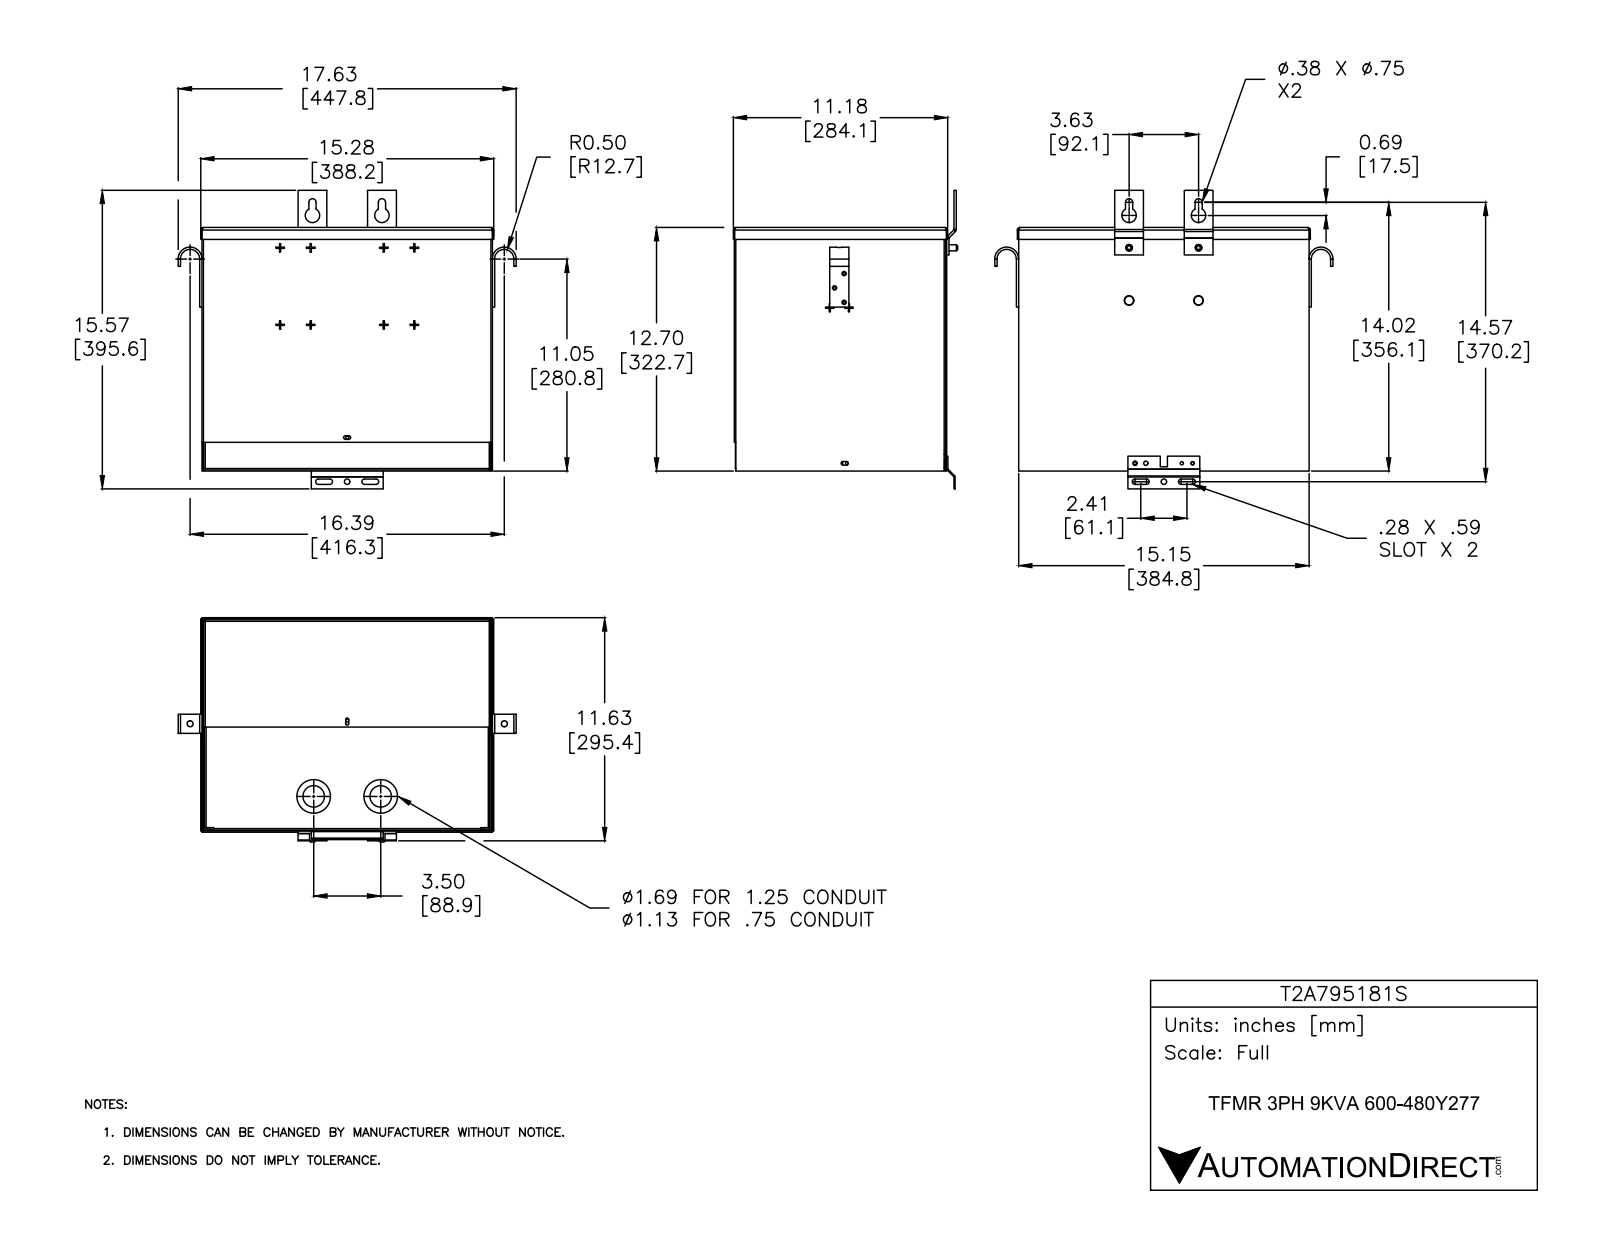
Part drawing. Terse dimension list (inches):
name: T2A795181S
written by: SolidWorks 2015 (AUTOMOTIVE_DESIGN)
unit: in
bodies: 12 solids, 707 faces (499 planar, 138 cylindrical, 70 other)
size: 17.63 × 15.574 × 11.697
volume: 66.19 in³; area: 2 202 in²
holes: 5× ⌀0.16, 4× ⌀0.313, 2× ⌀0.172, 2× ⌀0.219, 2× ⌀0.281, 2× ⌀0.344, 2× ⌀0.75, 2× ⌀1.125, 2× ⌀1.75, 1× ⌀0.173, 1× ⌀0.187
bosses: 2× ⌀1.81, 2× ⌀1.185, 2× ⌀0.312
rounds: 12× R0.015, 12× R0.075, 8× R0.094, 4× R0.075, 4× R0.135, 4× R0.141, 2× R0.02, 2× R0.03
face distances: 0.06, 11.02, 15.09, 10.96, 11.08, 12.52, 12.587, 0.067, 15.15, 15.03
hole spacings: 0.563, 1.342, 1.638, 1.688, 1.781, 2.014, 2.437, 3.625
